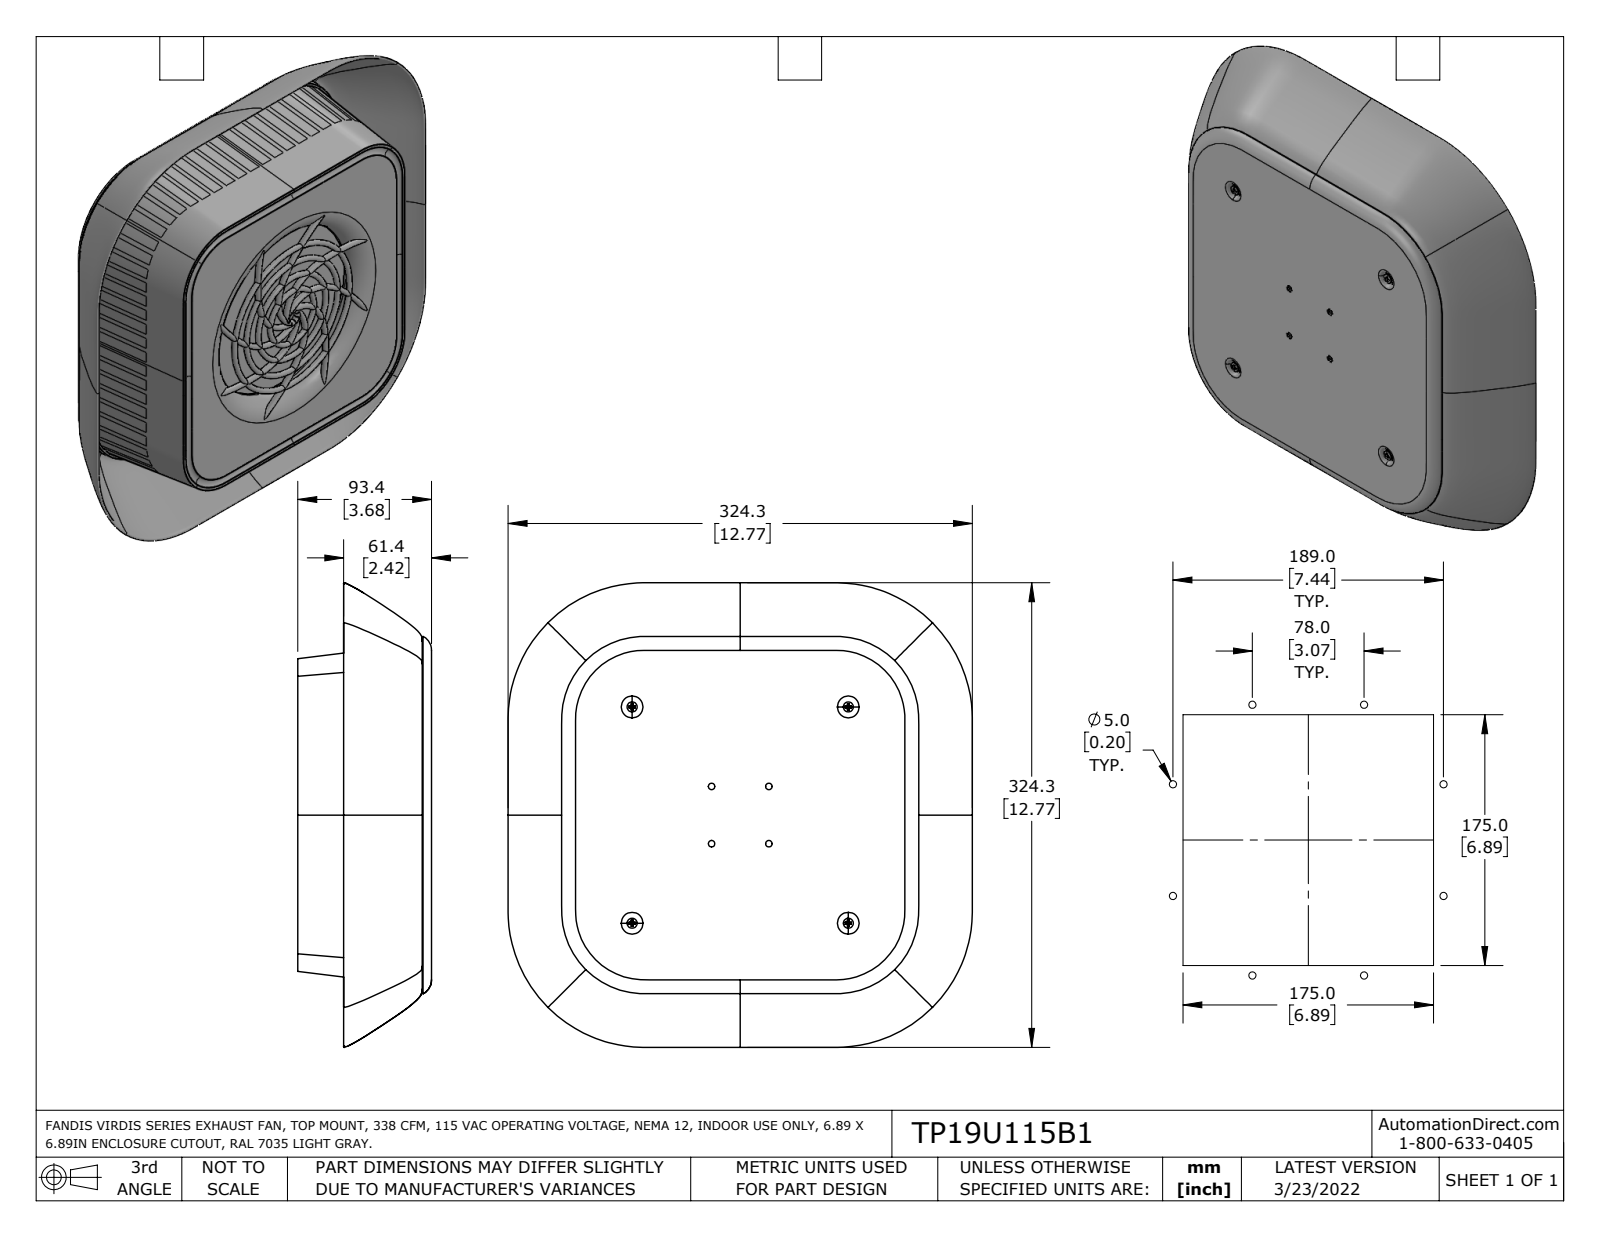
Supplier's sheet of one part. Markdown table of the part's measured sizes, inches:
| quantity | value |
| --- | --- |
| part name | TP19 |
| STEP written by | SolidWorks 2021 (AUTOMOTIVE_DESIGN) |
| units | inches |
| bodies | 1 solid, 475 faces (110 planar, 26 cylindrical, 339 other) |
| overall size | 12.769 × 12.769 × 3.682 |
| volume | 185.9 in³ |
| surface area | 673 in² |
| round holes (diameter × count) | 0.177 × 8, 5.188 × 1 |
| main face-to-face distances | 0.175, 0.059, 0.116, 3.682, 3.623, 3.507, 3.039, 2.98, 2.864, 0.644 |
| hole center spacings | 4.349, 1.113, 1.575, 3.09, 4.204, 5.317, 5.945, 2.227 |
